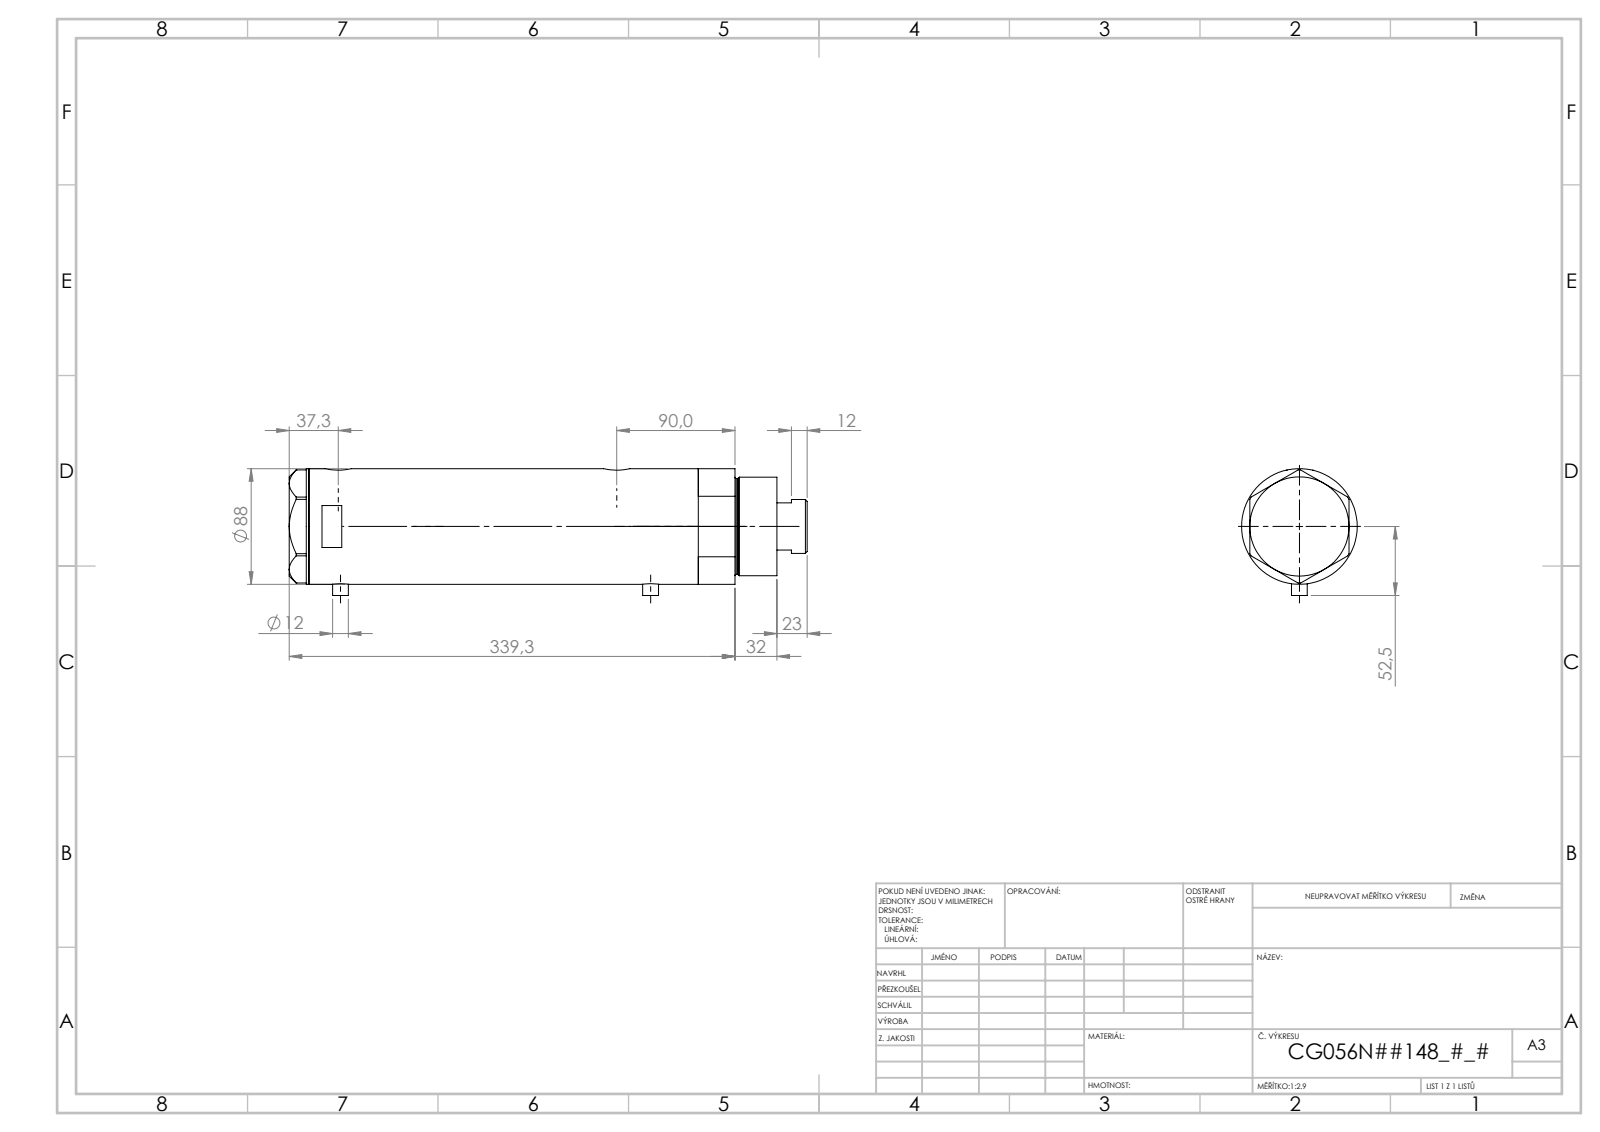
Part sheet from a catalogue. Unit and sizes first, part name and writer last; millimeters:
Units: millimetres
Overall size (bounding box): 394.3 × 96.5 × 88
Round holes (diameter × count): ⌀12.5 ×2, ⌀13.16 ×2, ⌀20 ×2, ⌀14.5 ×1, ⌀42 ×1, ⌀43.5 ×1, ⌀56 ×1, ⌀60 ×1, ⌀80 ×1
Round bosses / shafts (diameter × count): ⌀12 ×2, ⌀88 ×1, ⌀75 ×1, ⌀73 ×1, ⌀41 ×1
Main face-to-face distances: 234.4, 26, 208.4, 15, 41, 249.4, 356.3, 371.3, 330.3, 121.9
Hole centre spacings: 1.7, 25.8, 210.3, 212, 236.1, 237.8
Volume: 2 037 000 mm³ · Surface area: 279 956 mm²
Bodies: 4 solids, 121 faces (52 planar, 49 cylindrical, 20 other)
Part name (STEP PRODUCT): V270CG_VC; V270CG_MIDDLE; V270CG_BACK; V270CG_FRONT
STEP written by: SolidWorks 2019 (CONFIG_CONTROL_DESIGN)
